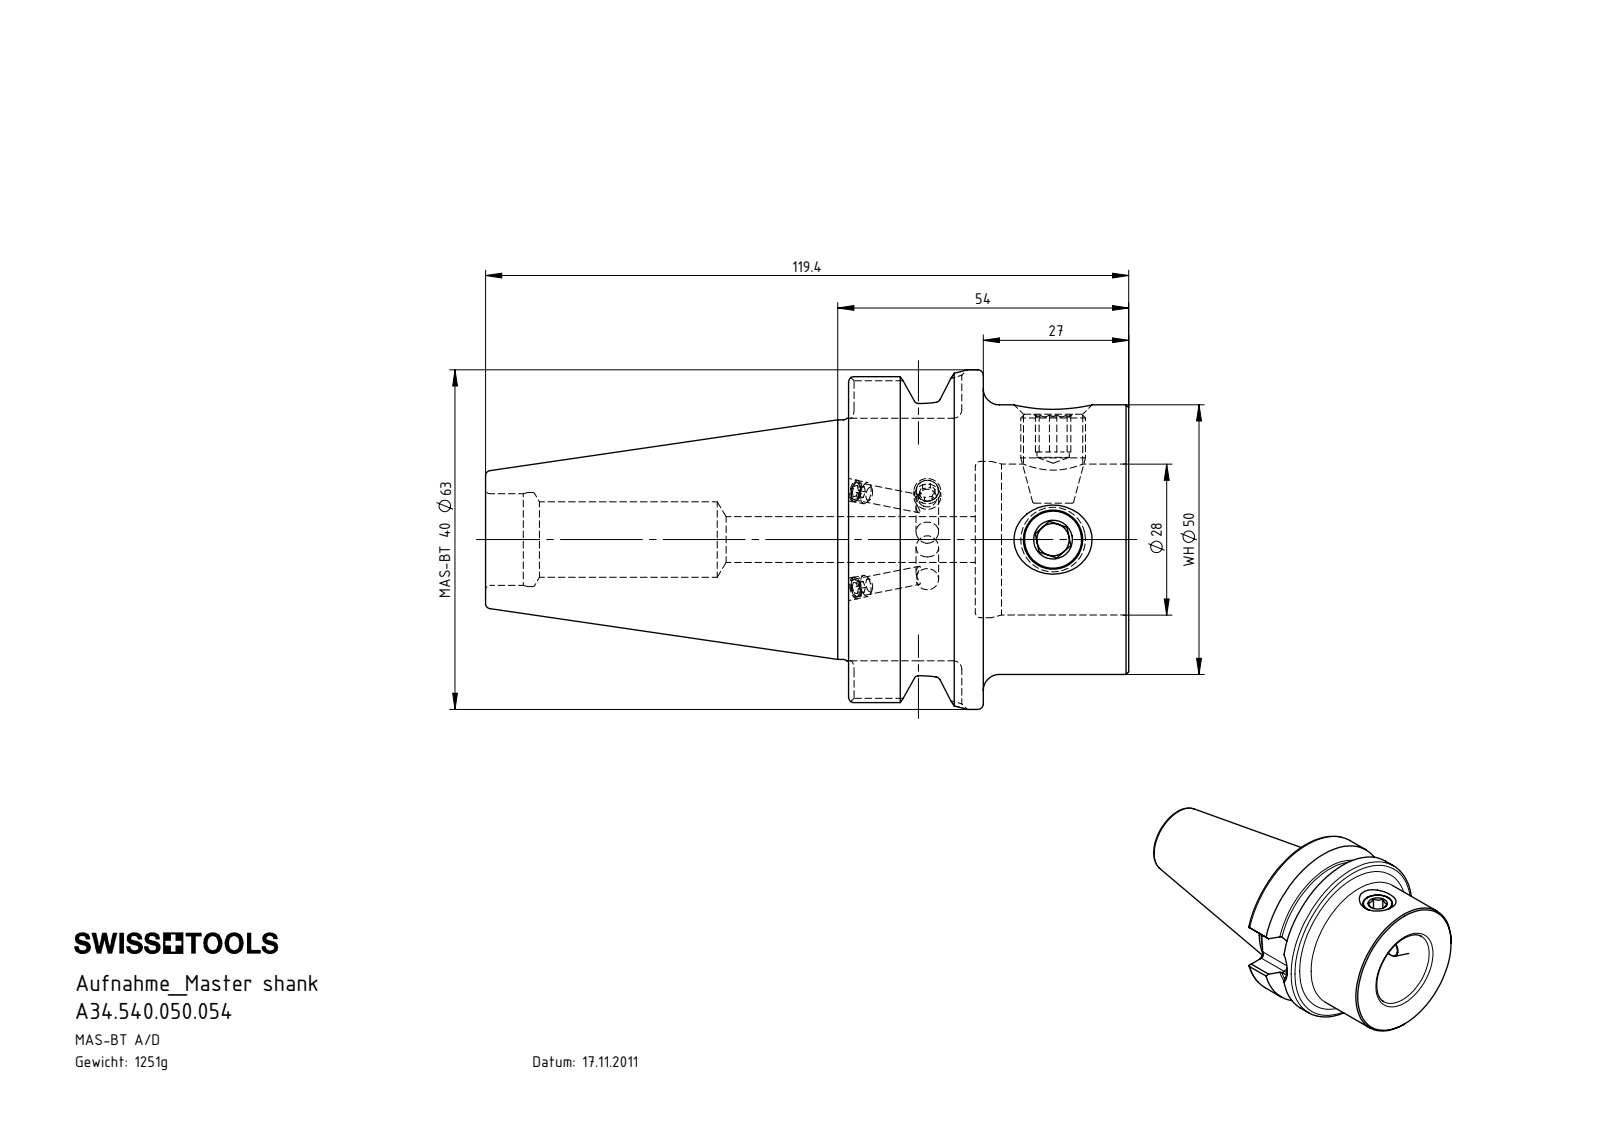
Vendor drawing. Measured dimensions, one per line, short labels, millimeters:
name: ISO 4026 - M4 x 3_PreviewCfg; WH5-ER1.001.017; ISO 4026 - M5 x 4_PreviewCfg; BB4-WH5.K01.054_C (+1 more)
written by: SolidWorks 2017 (AUTOMOTIVE_DESIGN)
unit: mm
bodies: 6 solids, 165 faces (75 planar, 39 cylindrical, 51 other)
size: 119.4 × 63 × 63
volume: 159 408 mm³; area: 30 989 mm²
holes: 2× ⌀3.3, 2× ⌀4.1, 2× ⌀6, 2× ⌀11, 1× ⌀4.2, 1× ⌀8.5, 1× ⌀14, 1× ⌀17, 1× ⌀17.45, 1× ⌀28, 1× ⌀29
bosses: 2× ⌀12, 2× ⌀4, 1× ⌀63, 1× ⌀53, 1× ⌀50, 1× ⌀44.45, 1× ⌀5
rounds: 8× R1.6, 1× R8.05
face distances: 52, 23.5, 28.5, 1.5, 25, 27, 45, 67.4, 90.9, 92.4
